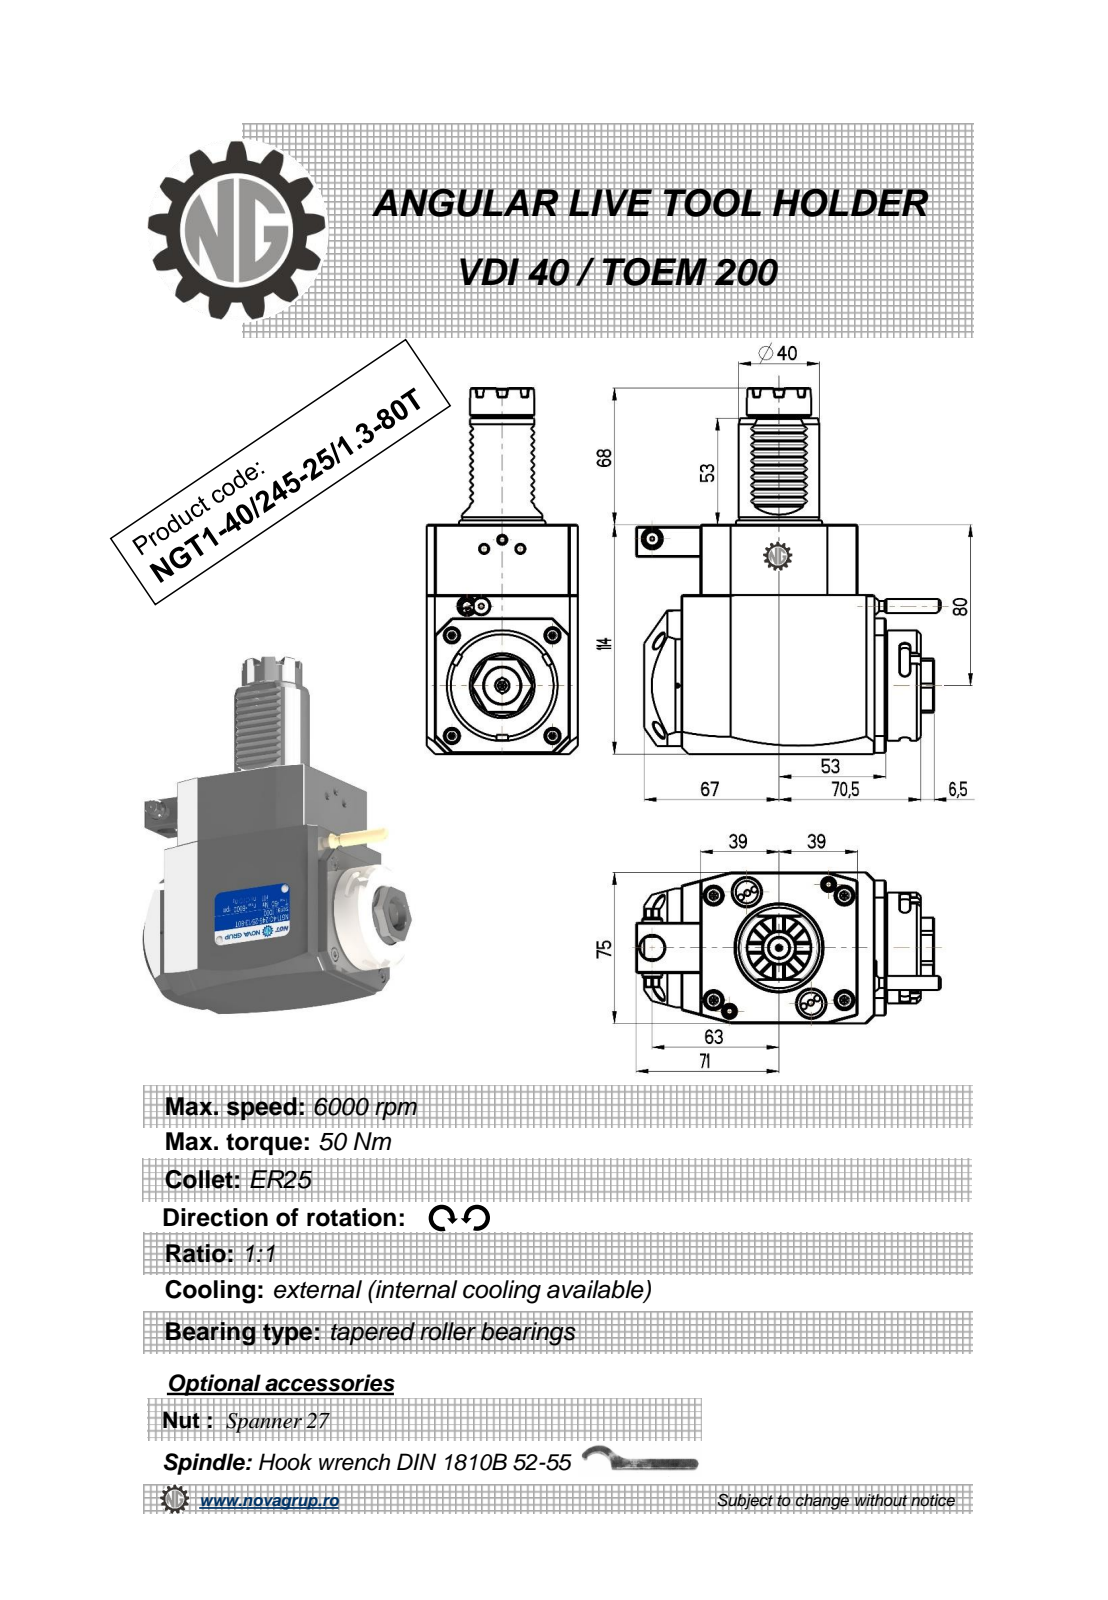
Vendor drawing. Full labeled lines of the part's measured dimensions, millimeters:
Part name (STEP PRODUCT): NGT1_40_245_25_1_3_80T
STEP written by: PRO/ENGINEER BY PARAMETRIC TECHNOLOGY CORPORATION, 2010280 (CONFIG_CONTROL_DESIGN)
Units: millimetres
Bodies: 1 solid, 474 faces (257 planar, 99 cylindrical, 118 other)
Overall size (bounding box): 182 × 151.33 × 75
Volume: 951 927 mm³ · Surface area: 72 295 mm²
Round holes (diameter × count): ⌀2 ×1, ⌀2.5 ×1, ⌀3 ×1, ⌀4.5 ×1, ⌀9.5 ×1, ⌀12 ×1, ⌀18 ×1
Round bosses / shafts (diameter × count): ⌀8 ×2, ⌀55 ×1, ⌀48 ×1, ⌀40 ×1, ⌀32 ×1, ⌀17.2 ×1, ⌀10 ×1, ⌀7 ×1
Partial cylindrical surfaces — rounded edges, fillets, slot ends (radius × count): R0.3 ×20, R2.5 ×6, R180 ×2, R3.85 ×1, R4.25 ×1, R15 ×1, R24.5 ×1, R37.5 ×1
Main face-to-face distances: 75, 114, 14, 17.5, 78, 92, 31.5, 109.5, 4, 28
Hole centre spacings: 37.35, 43.2, 72.5
